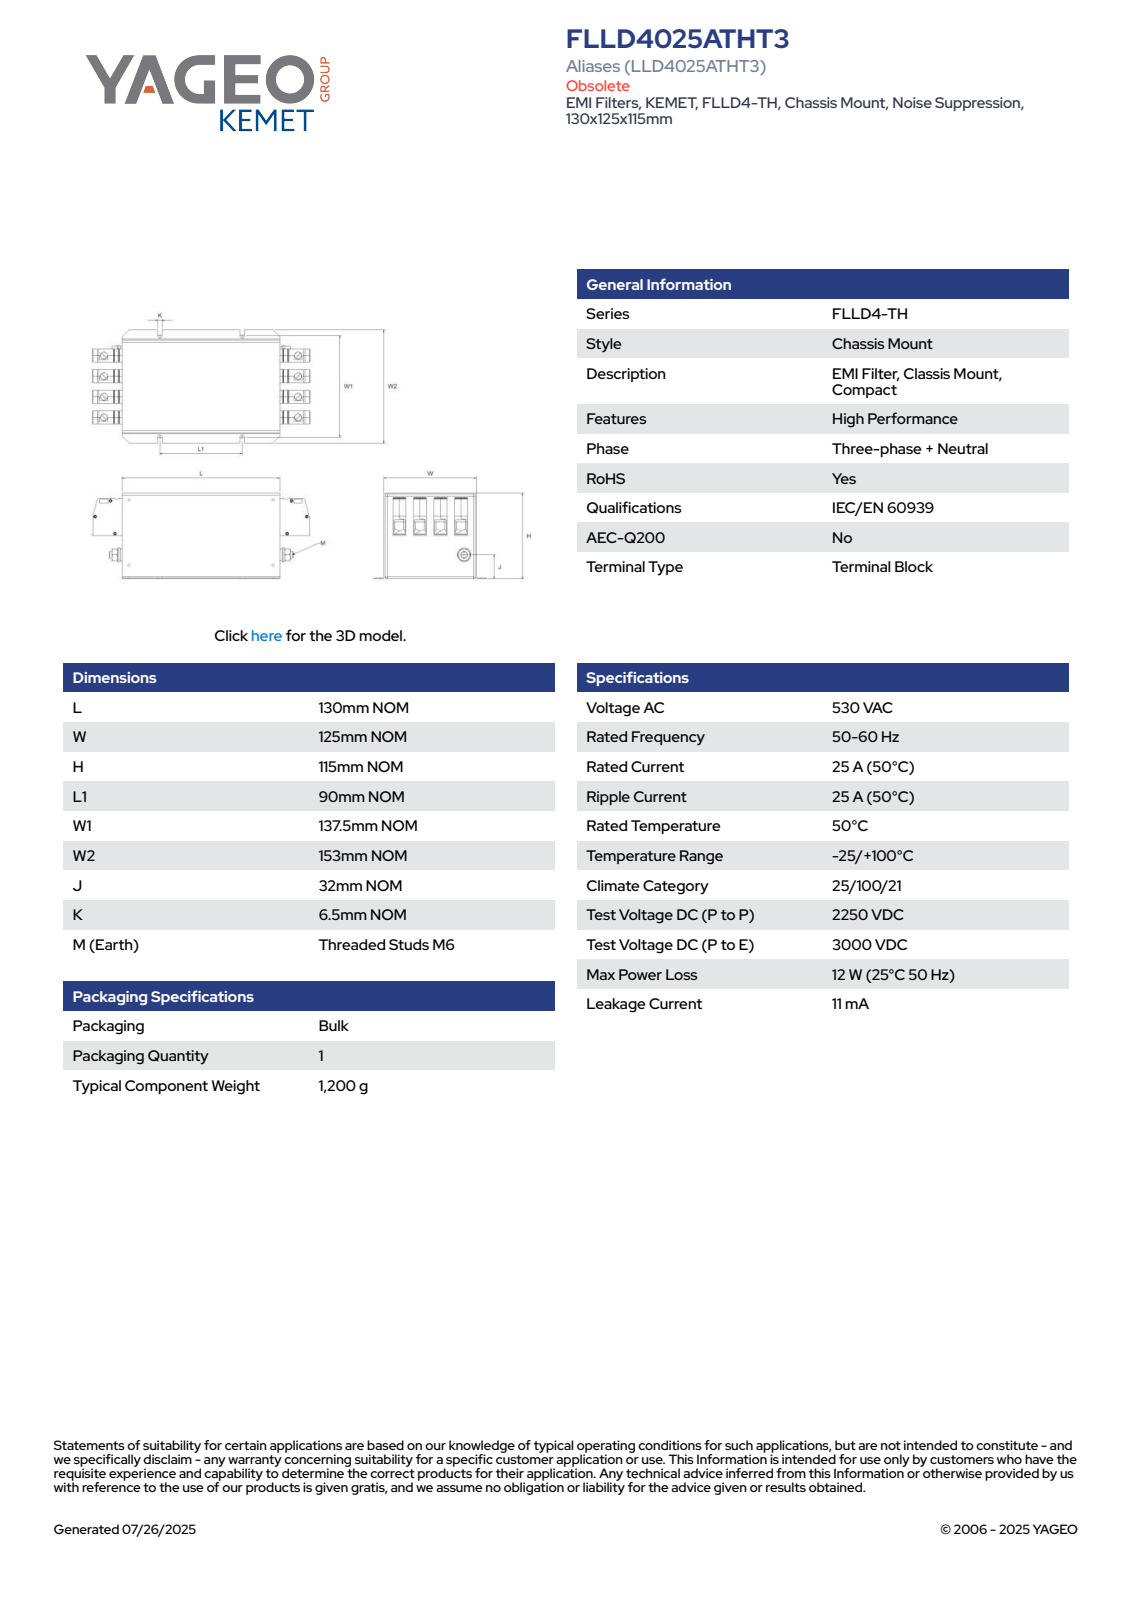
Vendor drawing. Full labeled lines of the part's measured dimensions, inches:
Part name (STEP PRODUCT): Earth connector M6 TH; plain washer grade a_din_Washer DIN 125 - A 6.4; hex nut style 1 gradeab_din_Hexagon Nut ISO 4032 - M6 - D - N; GEH0665 (+6 more)
STEP written by: SolidWorks 2014 (AUTOMOTIVE_DESIGN)
Units: inches
Bodies: 30 solids, 3709 faces (2286 planar, 1199 cylindrical, 224 other)
Overall size (bounding box): 6.488 × 6.024 × 4.528
Volume: 6.31 in³ · Surface area: 366.1 in²
Round holes (diameter × count): ⌀0.13 ×8, ⌀0.152 ×8, ⌀0.295 ×8, ⌀0.079 ×4, ⌀0.134 ×4, ⌀0.283 ×4, ⌀0.291 ×4, ⌀0.315 ×4, ⌀0.163 ×1, ⌀0.197 ×1, ⌀0.236 ×1, ⌀0.252 ×1
Round bosses / shafts (diameter × count): ⌀0.138 ×8, ⌀0.354 ×4, ⌀0.276 ×4, ⌀0.126 ×4, ⌀0.071 ×4, ⌀0.472 ×1, ⌀0.394 ×1, ⌀0.343 ×1
Partial cylindrical surfaces — rounded edges, fillets, slot ends (radius × count): R0.004 ×130, R0.008 ×41, R0.019 ×16, R0.051 ×16, R0.039 ×12, R0.079 ×12, R0.098 ×8, R0.128 ×4
Main face-to-face distances: 0.039, 4.488, 4.882, 5.079, 4.843, 4.528, 4.449, 5.118, 4.921, 5.039
Hole centre spacings: 0.591, 1.181, 0.699, 5.759, 0.374, 1.239, 1.772, 5.728
